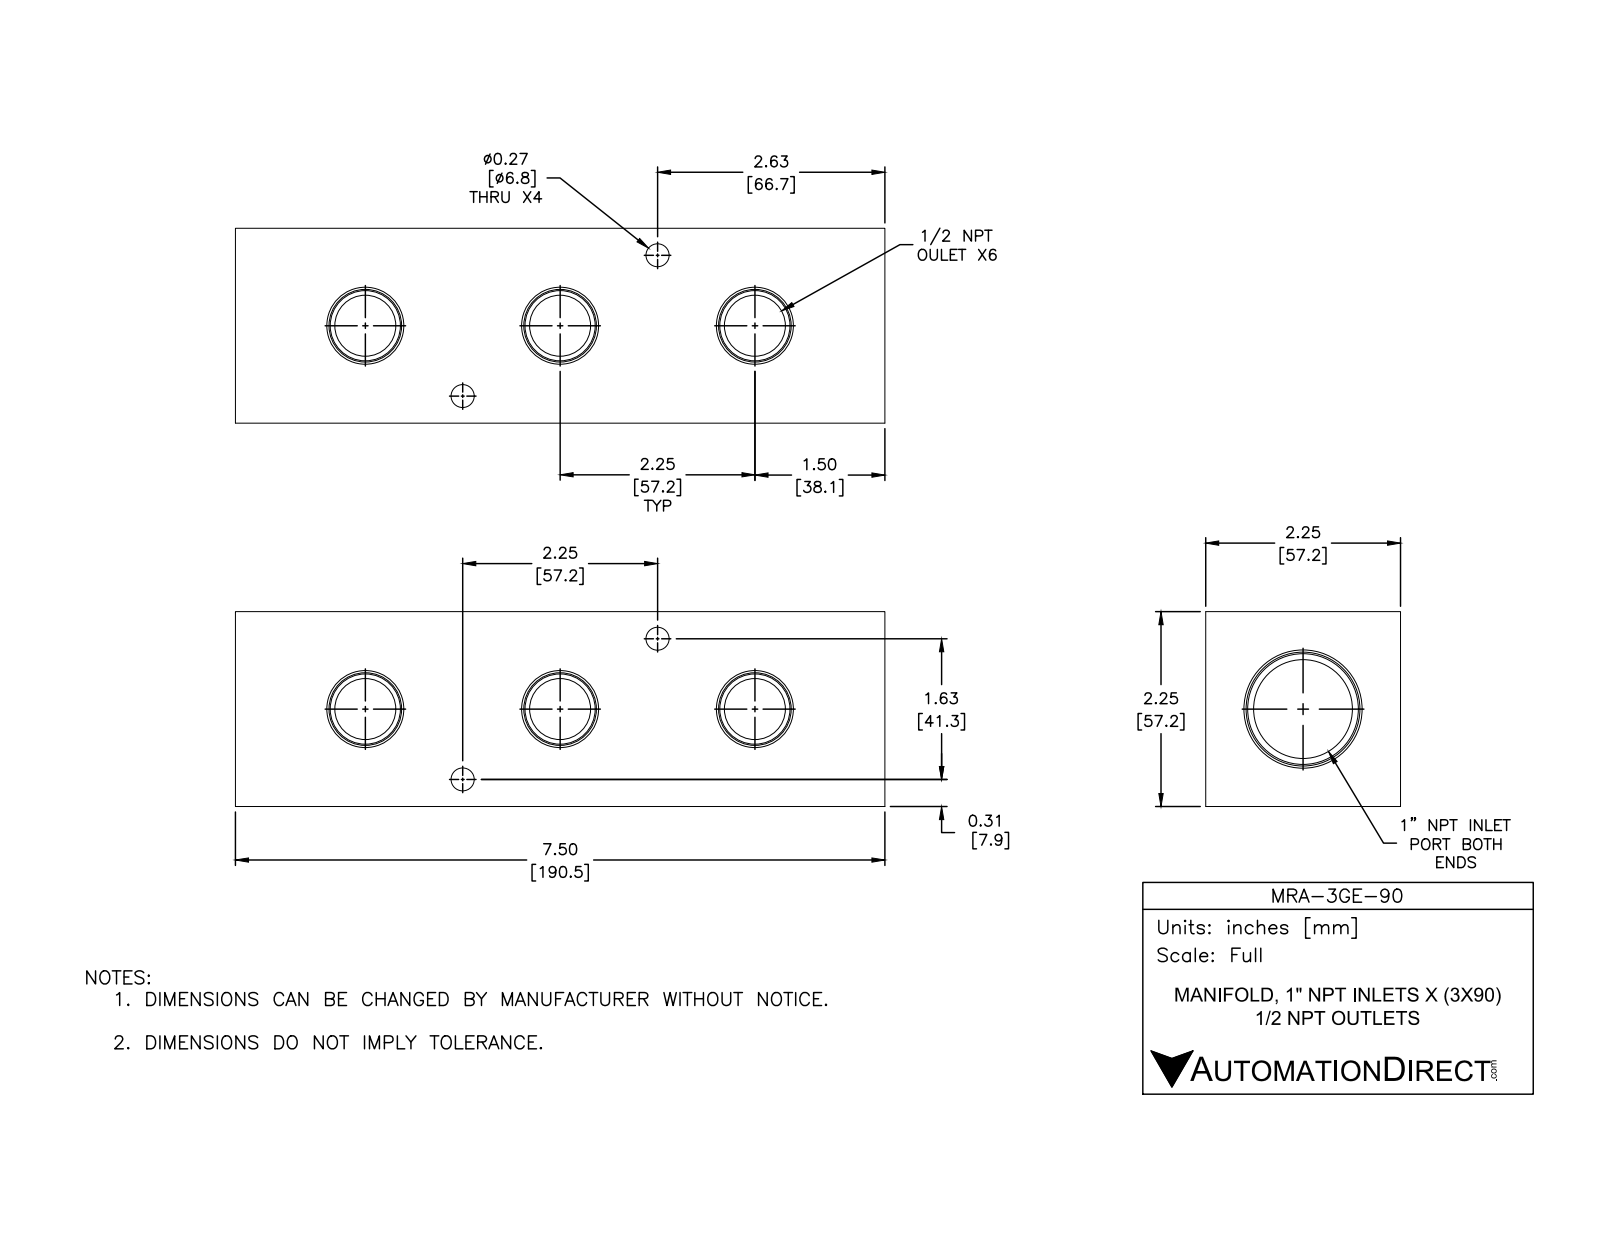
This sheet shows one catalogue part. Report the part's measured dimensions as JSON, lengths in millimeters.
{"part_name": "MRA-3GE-90", "step_written_by": "SolidWorks 2015 (CONFIG_CONTROL_DESIGN)", "units": "millimeters", "bodies": {"solids": 1, "faces": 76, "planar": 14, "cylindrical": 30, "other": 32}, "overall_size": [190.5, 57.2, 57.2], "volume_mm3": 452300, "surface_area_mm2": 73230, "round_holes": [[17.9, 6], [6.8, 4], [29, 1]], "face_to_face_distances": [57.2, 190.5, 13.5, 43.7, 16.8, 173.7, 157], "hole_center_spacings": [35.3, 57.2, 70.5, 88.2, 88.2, 114.3]}
